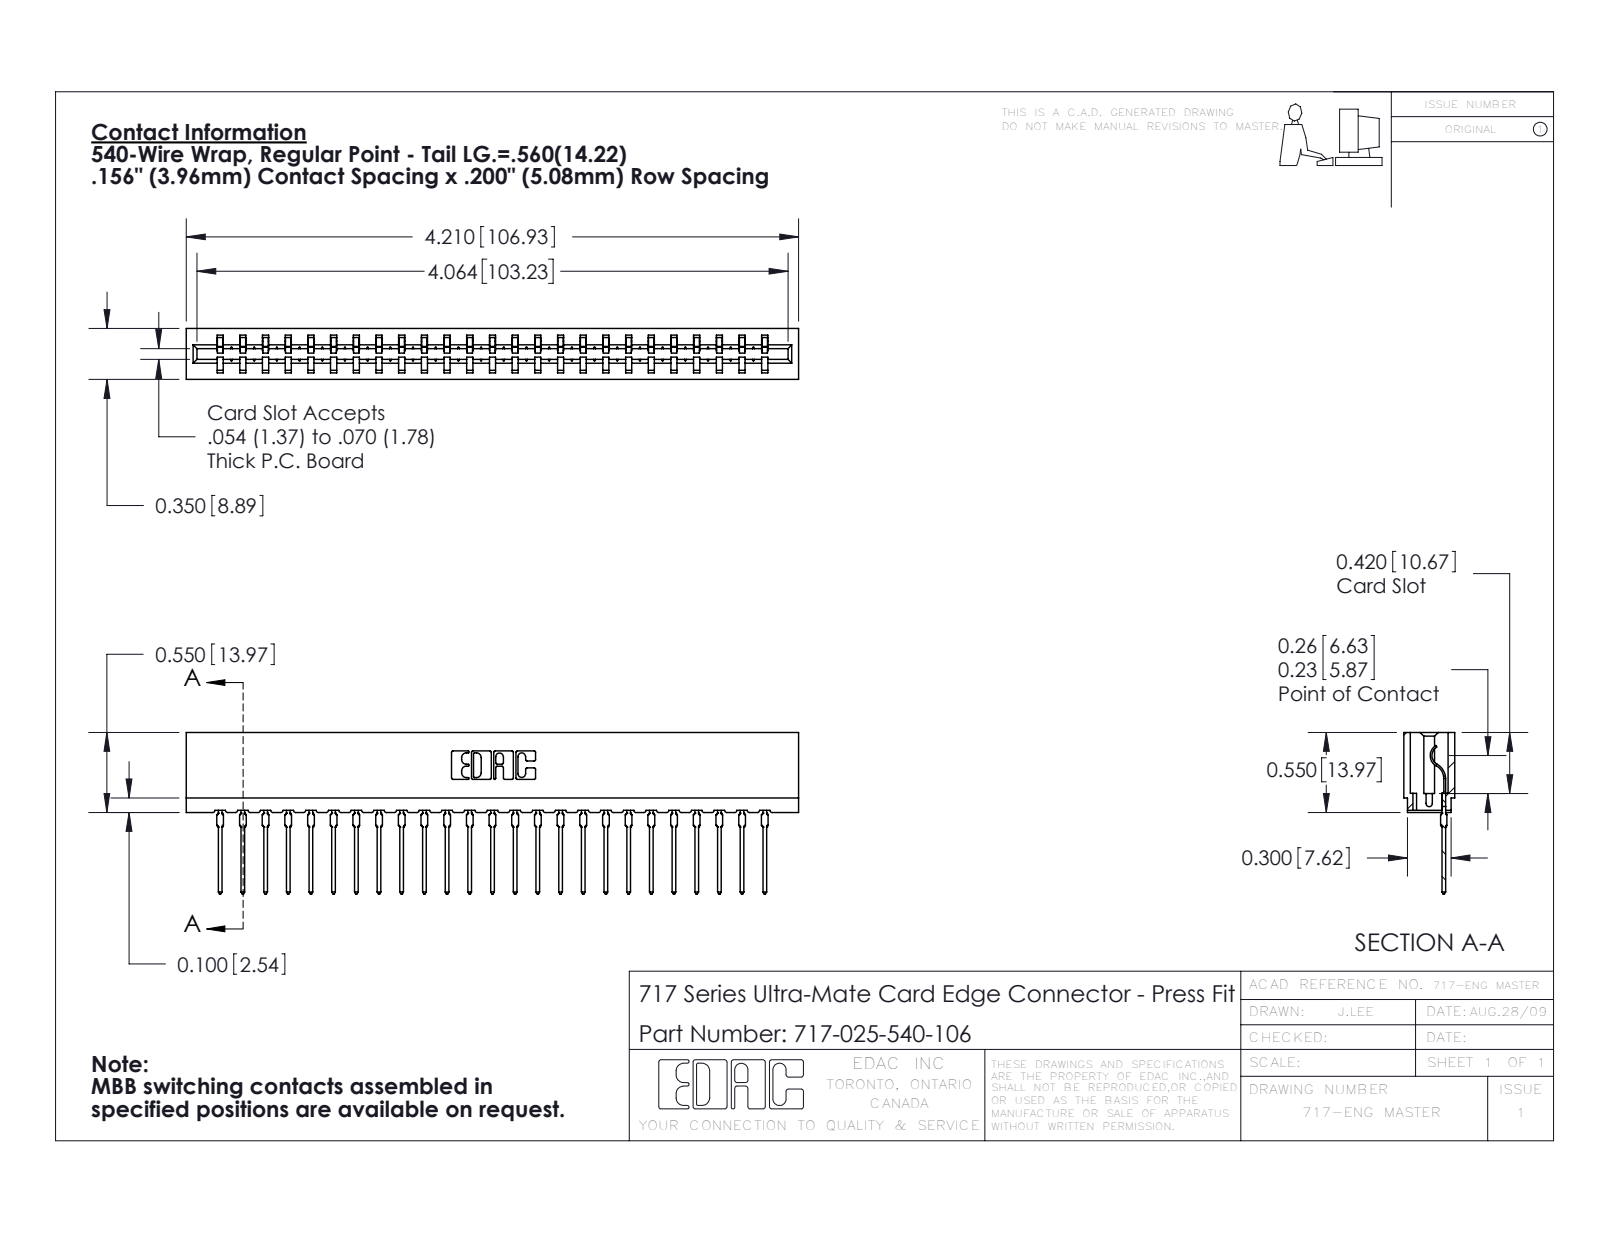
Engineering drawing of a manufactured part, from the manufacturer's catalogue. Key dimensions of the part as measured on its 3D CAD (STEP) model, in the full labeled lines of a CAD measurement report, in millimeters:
Part name (STEP PRODUCT): 717 Part_Insulator Option - 06; 717-025-540-106; 745-292-001_540
STEP written by: SolidWorks 2016 (CONFIG_CONTROL_DESIGN)
Units: millimetres
Bodies: 26 solids, 2919 faces (1754 planar, 515 cylindrical, 650 other)
Overall size (bounding box): 106.9 × 28.2 × 8.9
Volume: 9 160 mm³ · Surface area: 12 970 mm²
Partial cylindrical surfaces — rounded edges, fillets, slot ends (radius × count): R0.4 ×50, R0.5 ×50, R0.3 ×22, R0.2 ×6, R0.8 ×6, R0.1 ×4, R0.3 ×4, R0.7 ×3
Main face-to-face distances: 5.4, 3.5, 8.9, 4, 1.9, 1.6, 7.3, 1.9, 3.8, 15.8
